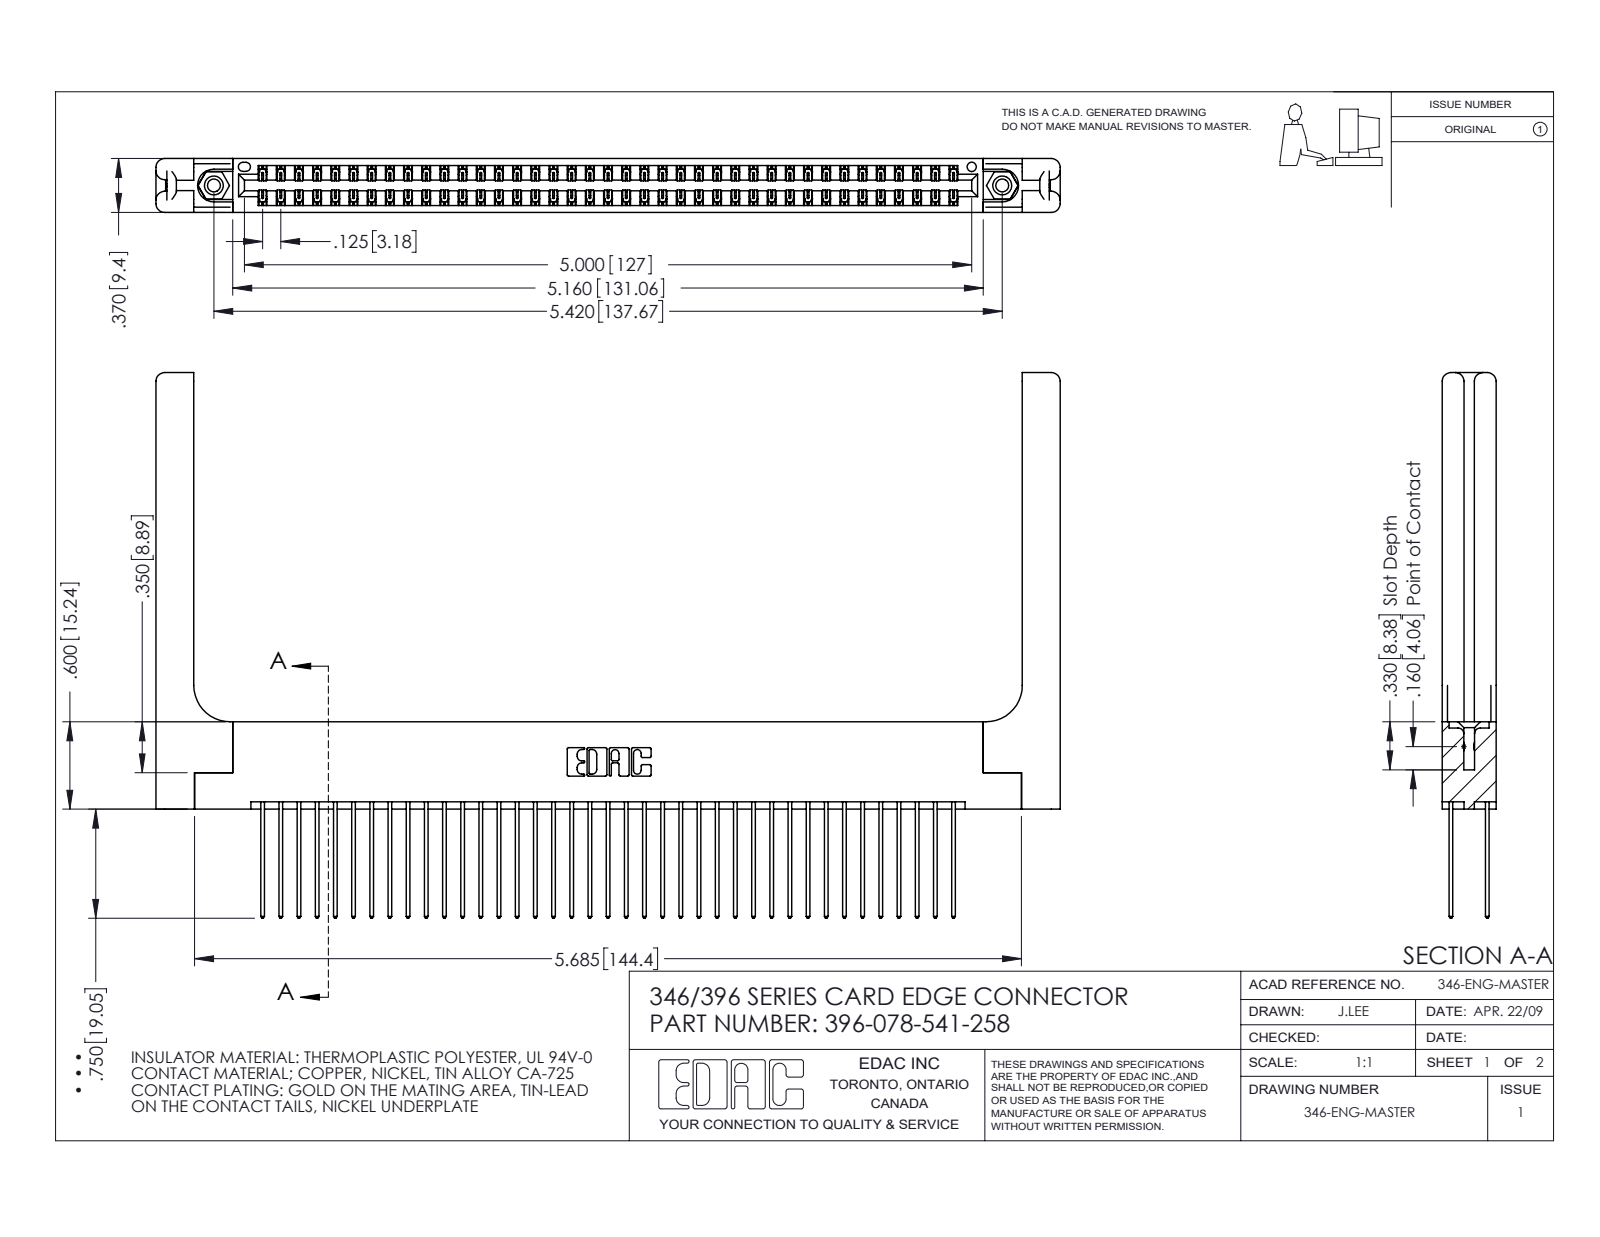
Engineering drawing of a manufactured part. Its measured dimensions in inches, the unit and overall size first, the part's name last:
Units: inches
Overall size (bounding box): 6.216 × 3.75 × 0.37
Round holes (diameter × count): ⌀0.089 ×2, ⌀0.125 ×2, ⌀0.156 ×2, ⌀0.064 ×1
Round bosses / shafts (diameter × count): ⌀0.155 ×2
Partial cylindrical surfaces — rounded edges, fillets, slot ends (radius × count): R0.006 ×117, R0.01 ×78, R0.01 ×22, R0.06 ×16, R0.007 ×6, R0.031 ×6, R0.026 ×3, R0.014 ×2
Main face-to-face distances: 0.048, 0.322, 0.072, 0.37, 0.25, 0.025, 0.298, 0.148, 0.15, 0.275
Hole centre spacings: 0.246, 5.211, 5.42
Volume: 1.423 in³ · Surface area: 44.67 in²
Bodies: 83 solids, 4434 faces (2954 planar, 1420 cylindrical, 60 other)
Part name (STEP PRODUCT): 345-250-001_345-250-001-102; 346-220-058_345-220-058; 345-292-001_345-293-141; 346 Part_Flush Mounting Lugs - 0.156 Dia-TH (+1 more)
STEP written by: SolidWorks 2016 (CONFIG_CONTROL_DESIGN)
